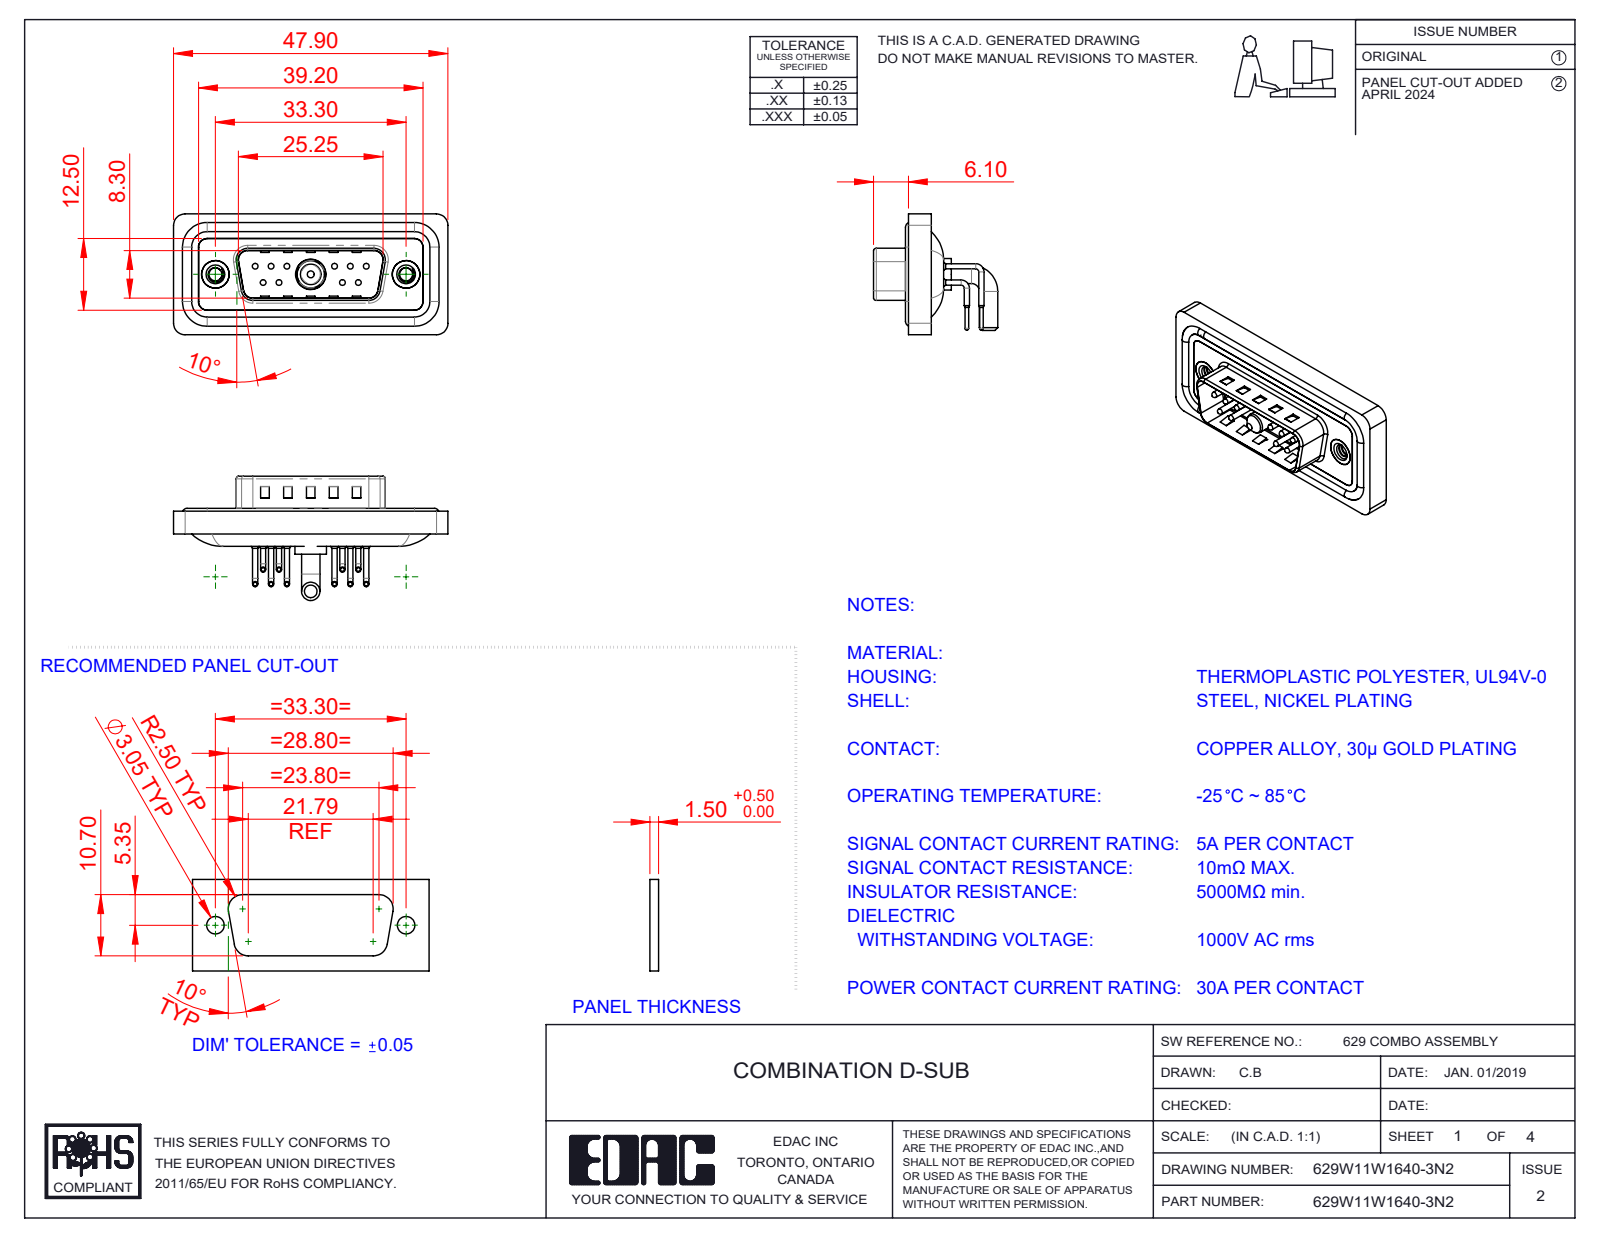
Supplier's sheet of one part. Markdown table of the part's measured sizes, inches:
| quantity | value |
| --- | --- |
| part name | Power Pin_30A RA; 629Combo Contact Row 1; 629Combo Housing_11W1; 629Combo Shell Front_15 Contacts (+5 more) |
| STEP written by | SolidWorks 2023 (CONFIG_CONTROL_DESIGN) |
| units | inches |
| bodies | 19 solids, 1603 faces (836 planar, 569 cylindrical, 198 other) |
| overall size | 1.886 × 0.854 × 0.831 |
| volume | 0.343 in³ |
| surface area | 14.41 in² |
| round holes (diameter × count) | 0.03 × 10, 0.063 × 10, 0.079 × 10, 0.089 × 2, 0.157 × 2, 0.189 × 2, 0.197 × 2, 0.191 × 1, 0.209 × 1 |
| round bosses / shafts (diameter × count) | 0.035 × 20, 0.059 × 10, 0.039 × 10, 0.026 × 10, 0.063 × 4, 0.193 × 2, 0.126 × 2, 0.217 × 1 |
| partial cylindrical surfaces (radius × count) | 0.079 × 20, 0.059 × 18, 0.04 × 10, 0.02 × 8, 0.063 × 8, 0.039 × 7, 0.01 × 4, 0.024 × 4 |
| main face-to-face distances | 0.016, 0.114, 0.031, 0.043, 0.083, 0.063, 0.098, 0.161, 0.177, 0.122 |
| hole center spacings | 0.124, 0.109, 0.545, 0.436, 0.654, 0.198, 0.198, 0.218 |
